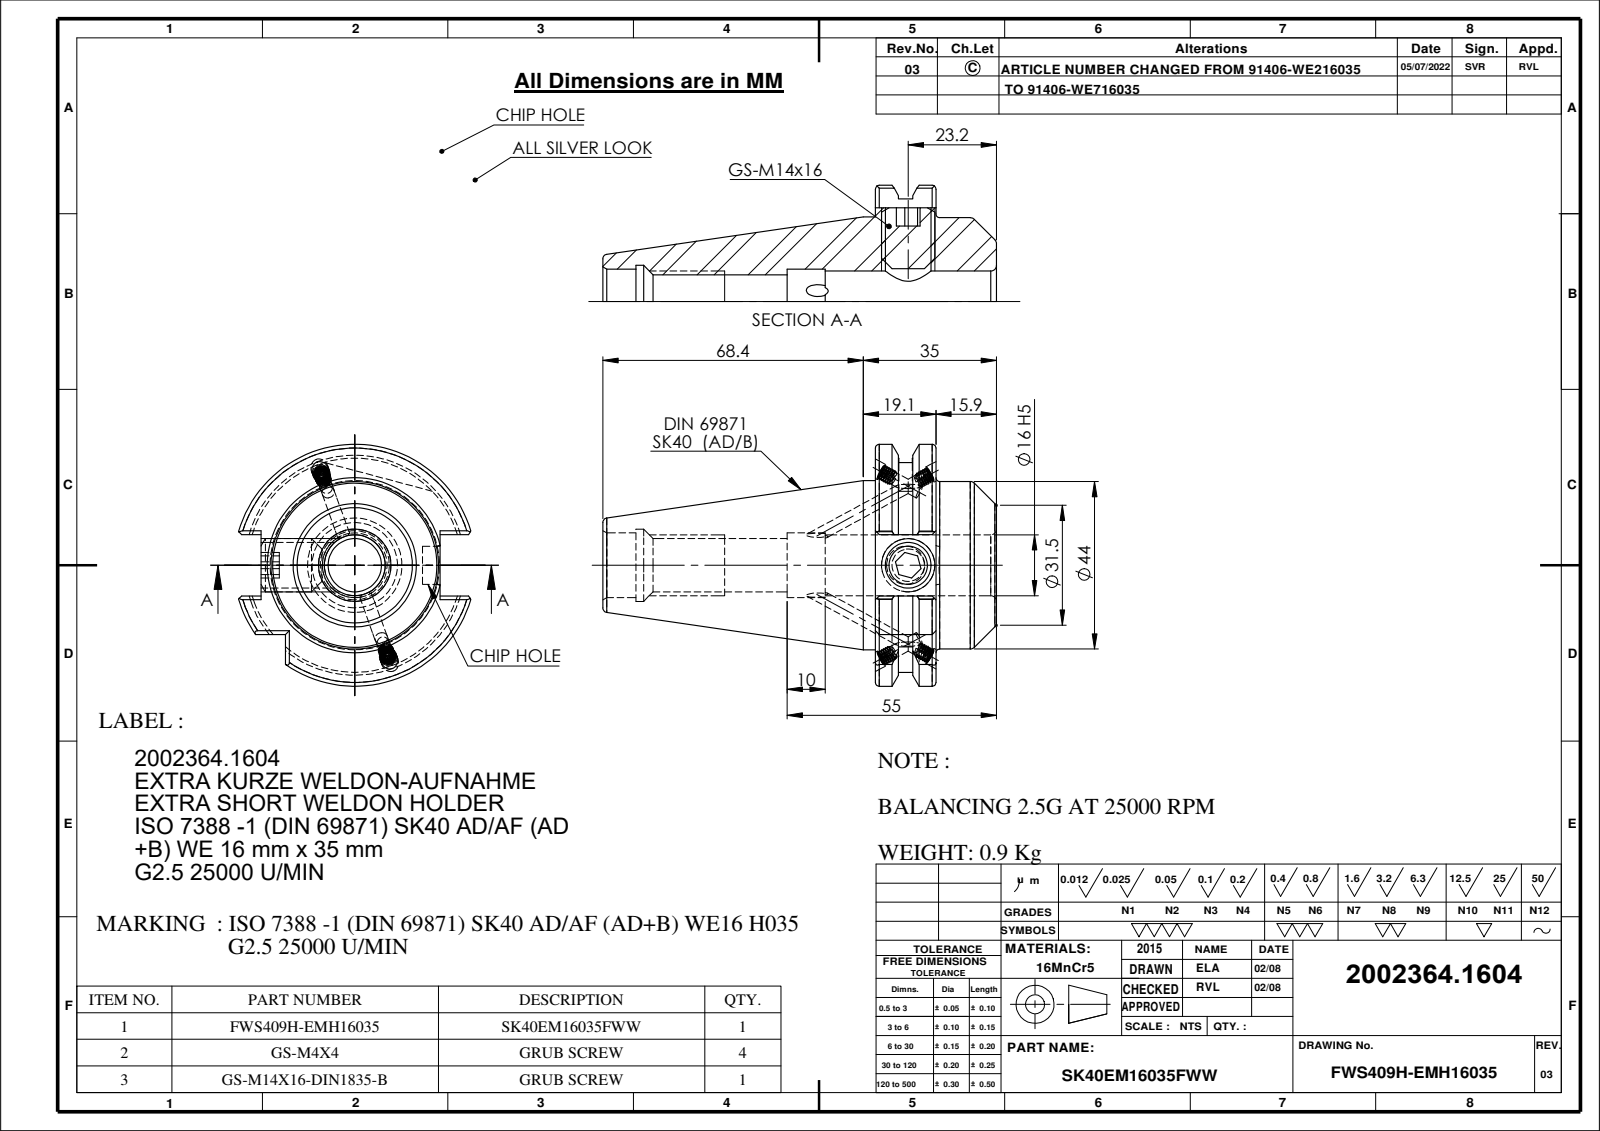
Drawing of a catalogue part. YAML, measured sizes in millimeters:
part_name: "SK40EM16035FWW R01; GS-M4X4_DIN 913 - M4 x 4-N; GS-M14X16-DIN1835-B_ISO 4026 - M12 x 12-N; 91406-WE716035"
step_written_by: "SolidWorks 2018 (CONFIG_CONTROL_DESIGN)"
units: millimeters
bodies: {solids: 6, faces: 345, planar: 97, cylindrical: 96, other: 152}
overall_size: [103.4, 63.55, 61]
volume: 114237
surface_area: 25944
round_holes:
  - {diameter: 3.3, count: 4}
  - {diameter: 4.5, count: 4}
  - {diameter: 10, count: 1}
  - {diameter: 12, count: 1}
  - {diameter: 14, count: 1}
  - {diameter: 16, count: 1}
  - {diameter: 17, count: 1}
  - {diameter: 19, count: 1}
round_bosses_or_shafts:
  - {diameter: 4, count: 4}
  - {diameter: 44.45, count: 1}
  - {diameter: 44, count: 1}
  - {diameter: 14, count: 1}
partial_cylinders:
  - {radius: 28.12, count: 1}
  - {radius: 31.77, count: 1}
face_to_face_distances: [15.9, 31.8, 47, 16.1, 71.6, 87.5, 103.4, 77.65, 6.05, 9.85]
hole_center_spacings: [38.16, 0.65]
